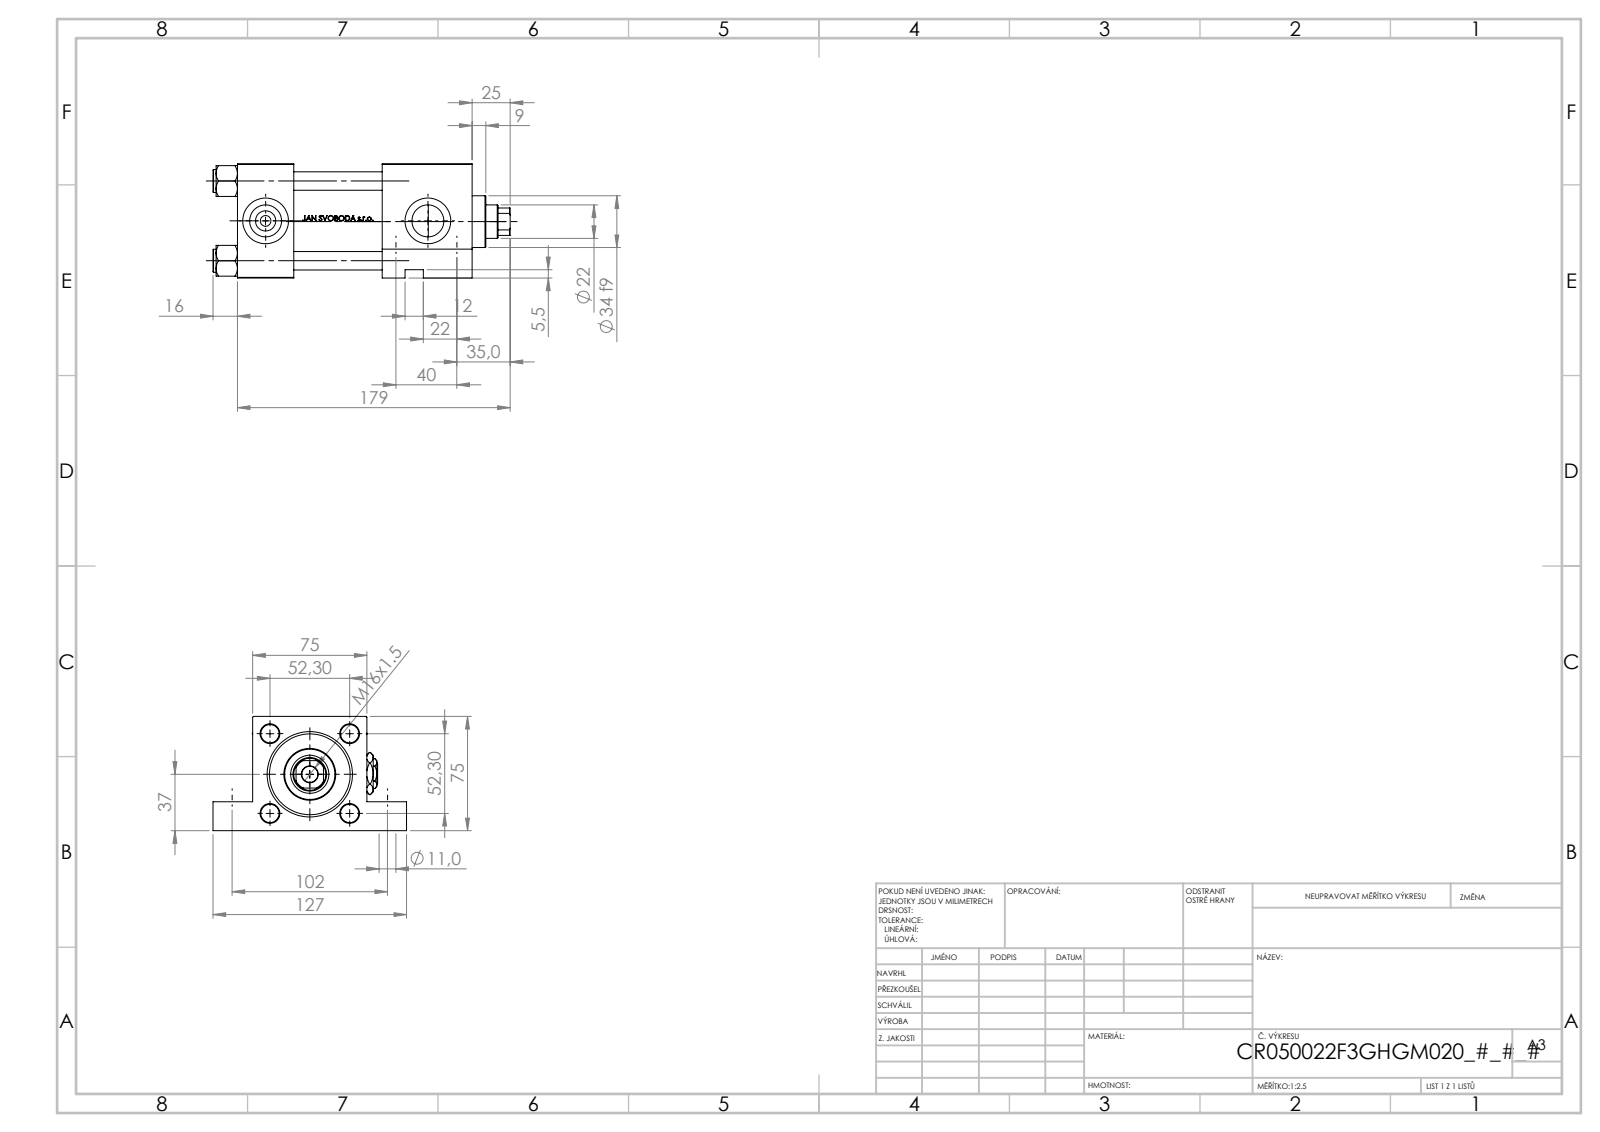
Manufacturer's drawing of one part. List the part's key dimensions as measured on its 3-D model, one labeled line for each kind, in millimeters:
Part name (STEP PRODUCT): NUT_M5_F; V215CR_VCP_F; V215CR_F_Body; Zatka_pro_OIL_PORT (+2 more)
STEP written by: SolidWorks 2019 (CONFIG_CONTROL_DESIGN)
Units: millimetres
Bodies: 13 solids, 1199 faces (483 planar, 134 cylindrical, 582 other)
Overall size (bounding box): 195 × 127 × 75
Volume: 702 130 mm³ · Surface area: 160 606 mm²
Round holes (diameter × count): ⌀12 ×4, ⌀20.96 ×3, ⌀30 ×3, ⌀7 ×2, ⌀11 ×2, ⌀11 ×2, ⌀10.5 ×1, ⌀17 ×1, ⌀22 ×1, ⌀25 ×1, ⌀41 ×1, ⌀50 ×1
Round bosses / shafts (diameter × count): ⌀15 ×4, ⌀56 ×1, ⌀34 ×1
Partial cylindrical surfaces — rounded edges, fillets, slot ends (radius × count): R10.5 ×1
Main face-to-face distances: 75, 37, 154, 117, 95, 58, 59, 19, 56, 125.3
Hole centre spacings: 52.3, 36.63, 37.34, 40, 73.96, 102, 109.56, 13
